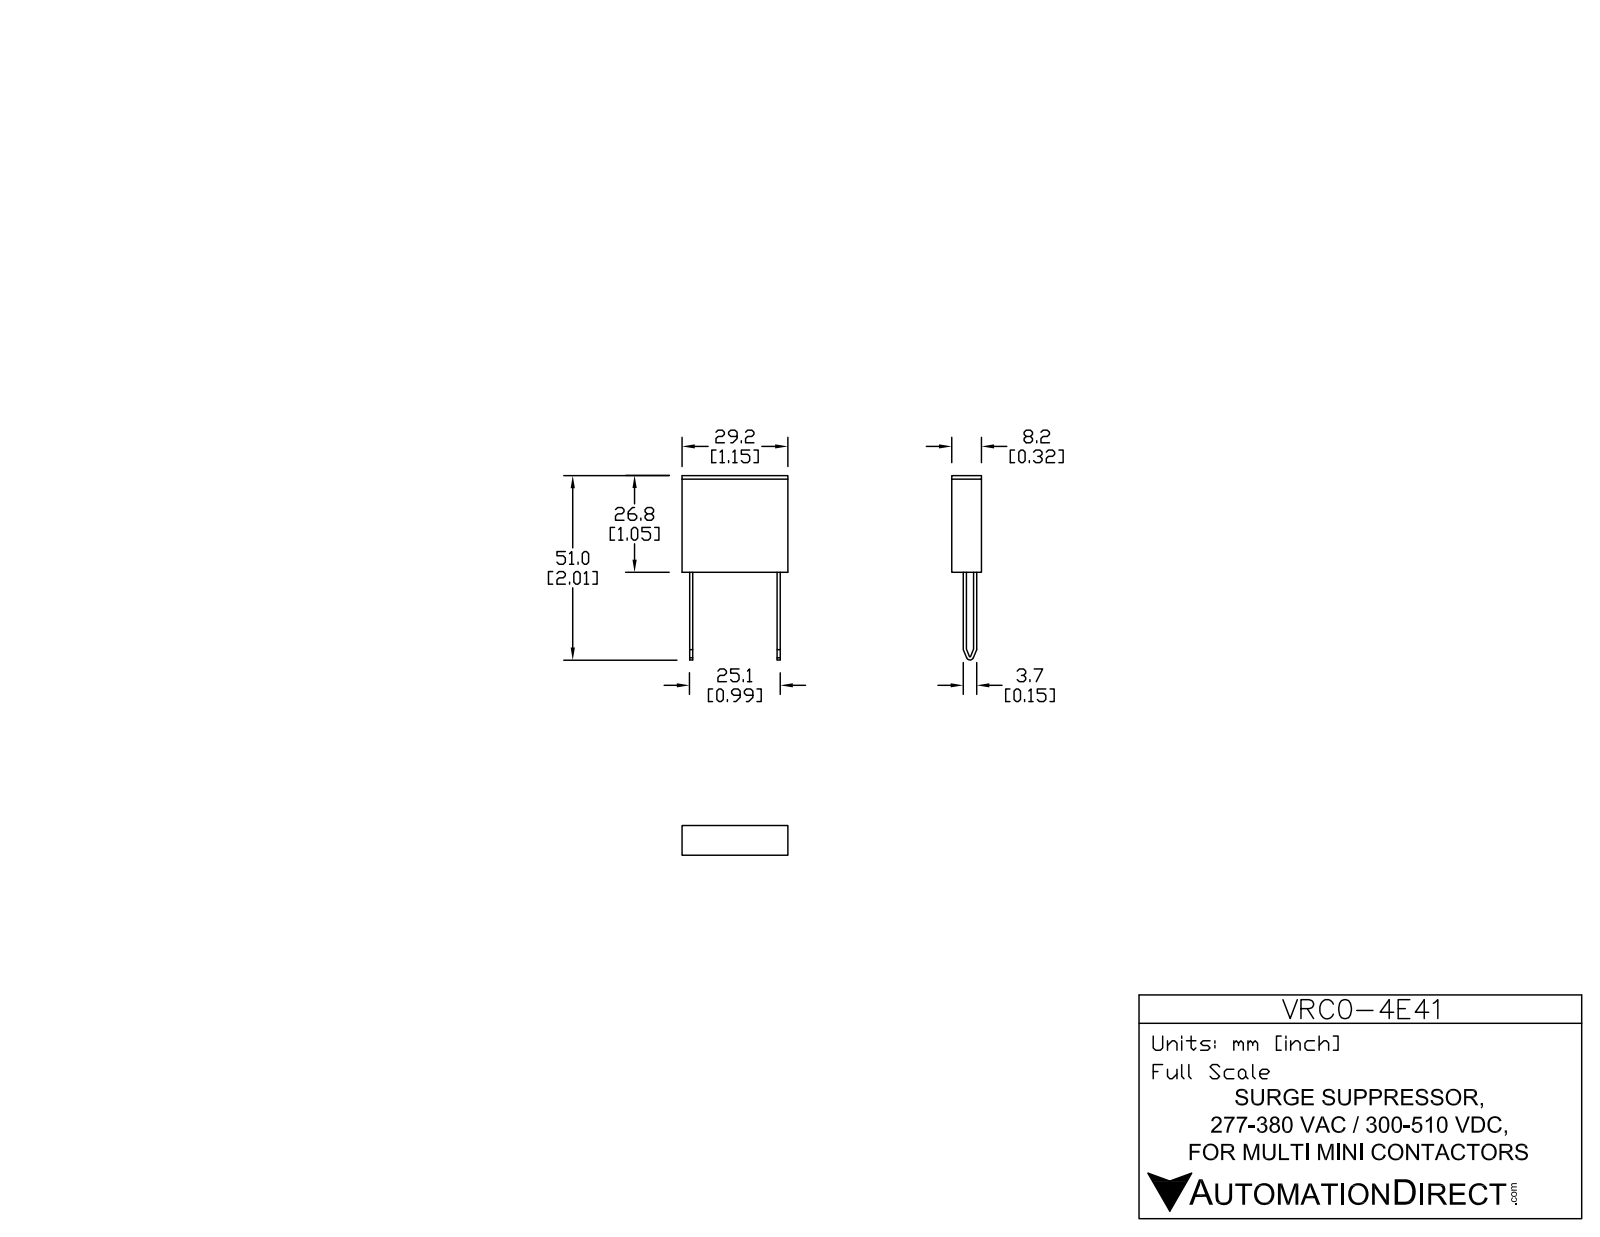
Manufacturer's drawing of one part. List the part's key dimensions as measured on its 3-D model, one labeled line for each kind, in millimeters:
Part name (STEP PRODUCT): VRC0-4E41
STEP written by: SolidWorks 2013 (AUTOMOTIVE_DESIGN)
Units: millimetres
Bodies: 1 solid, 34 faces (26 planar, 8 cylindrical, 0 other)
Overall size (bounding box): 50.9 × 29.2 × 8.2
Volume: 6 463 mm³ · Surface area: 2 803 mm²
Partial cylindrical surfaces — rounded edges, fillets, slot ends (radius × count): R0.15 ×1, R1 ×1
Main face-to-face distances: 8.2, 26.7, 29.2, 0.85, 2.1, 27.1, 2.95, 26.25, 24.15, 2.85
